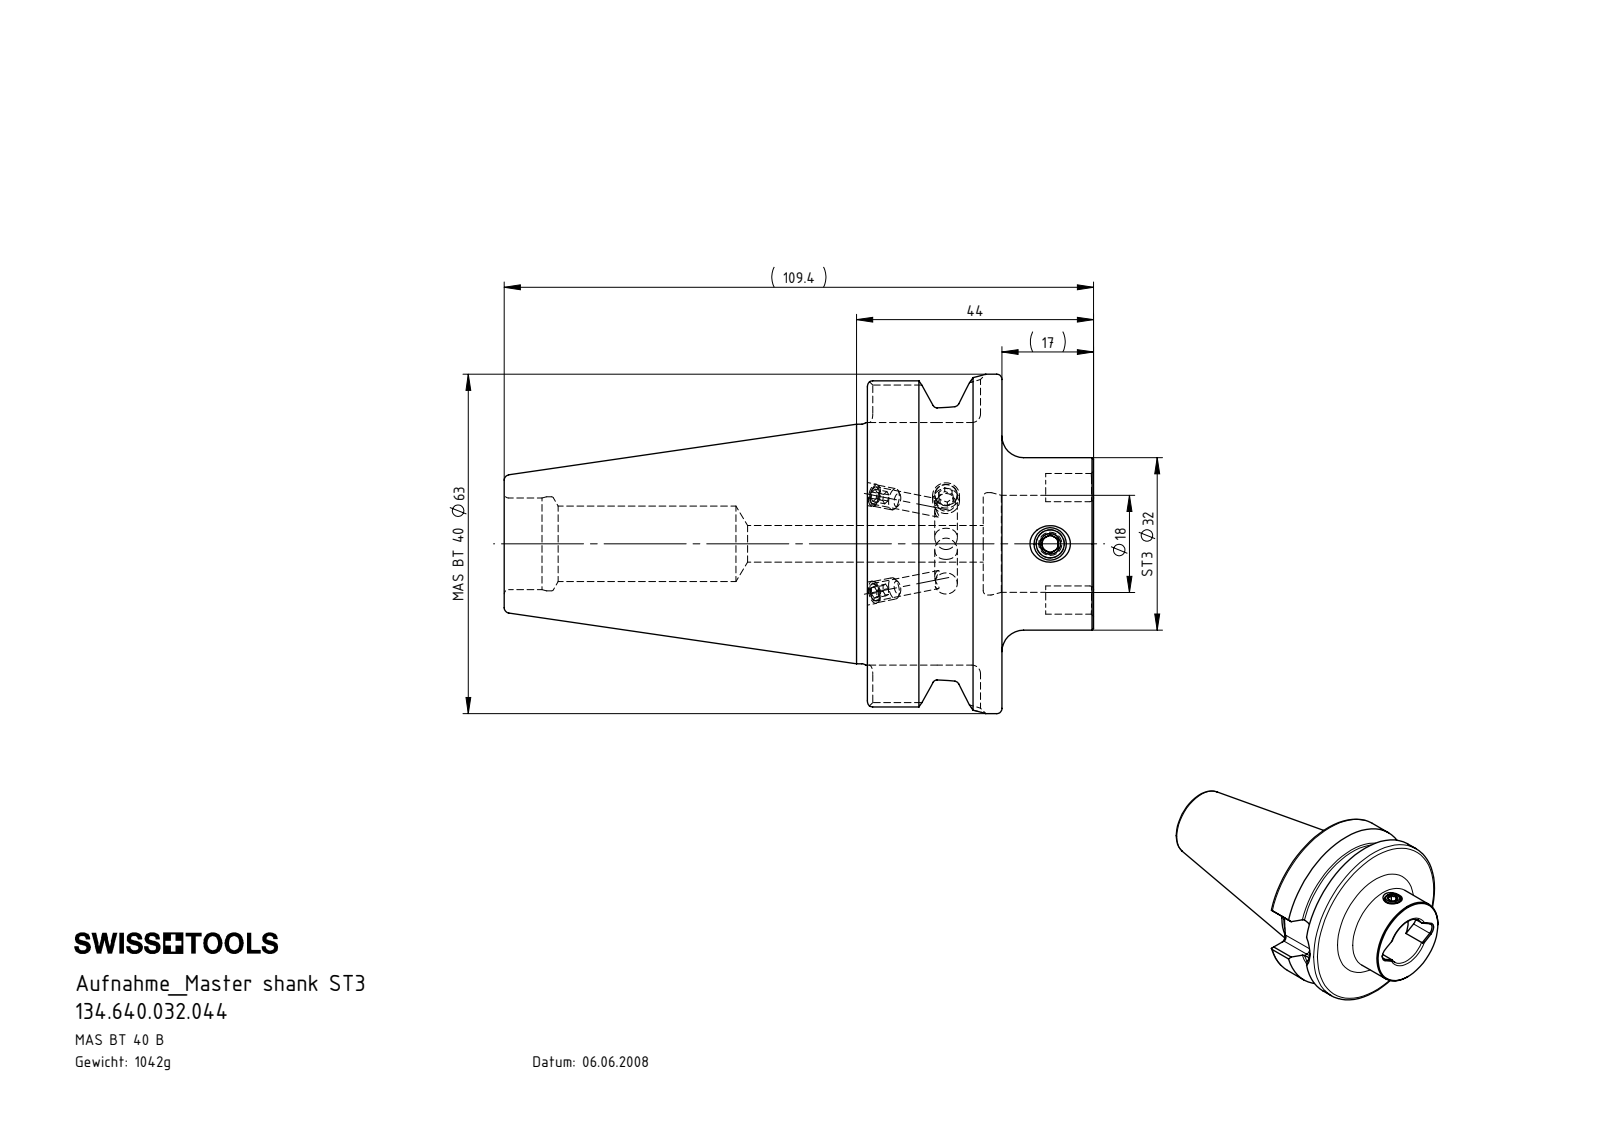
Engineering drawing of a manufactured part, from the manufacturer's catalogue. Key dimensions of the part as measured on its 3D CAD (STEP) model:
Part name (STEP PRODUCT): ST3-ER1.001.008_A; ISO 4026 - M5 x 4; BB4-ST3.K01.044; BB4-ST3.K01.044_A_mit Bundkhlung
STEP written by: SolidWorks 2015 (CONFIG_CONTROL_DESIGN)
Units: millimetres
Bodies: 3 solids, 170 faces (45 planar, 55 cylindrical, 70 other)
Overall size (bounding box): 109.4 × 63 × 63
Volume: 132 631 mm³ · Surface area: 25 168 mm²
Round holes (diameter × count): ⌀4 ×2, ⌀4.2 ×1, ⌀5.25 ×1, ⌀6.8 ×1, ⌀14 ×1, ⌀17 ×1, ⌀17.45 ×1, ⌀18 ×1, ⌀19 ×1
Round bosses / shafts (diameter × count): ⌀63 ×1, ⌀53 ×1, ⌀44.45 ×1, ⌀32 ×1, ⌀6 ×1, ⌀5 ×1
Partial cylindrical surfaces — rounded edges, fillets, slot ends (radius × count): R1.6 ×8, R2.5 ×2, R8.05 ×1
Main face-to-face distances: 25, 42, 17, 45, 21.5, 3.5, 20.5, 67.4, 88.9, 92.4
